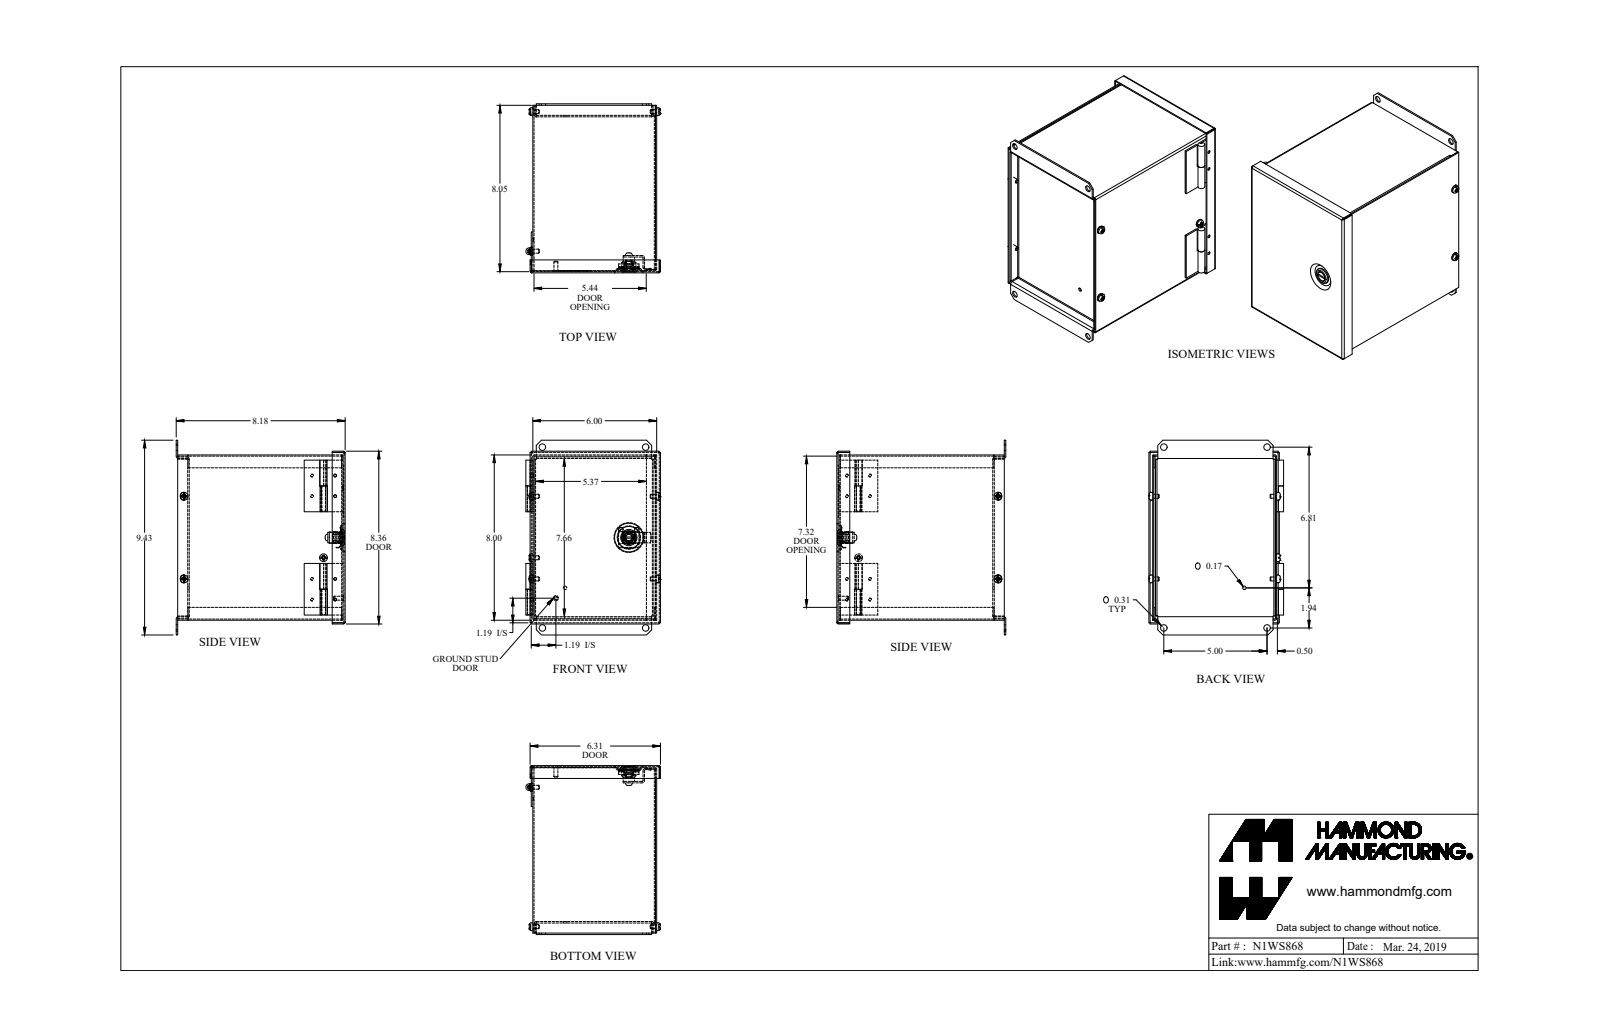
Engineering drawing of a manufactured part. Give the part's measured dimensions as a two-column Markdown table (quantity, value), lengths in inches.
| quantity | value |
| --- | --- |
| part name | N1WS868 |
| STEP written by | SolidWorks 2018 (AUTOMOTIVE_DESIGN) |
| units | inches |
| bodies | 15 solids, 539 faces (290 planar, 196 cylindrical, 53 other) |
| overall size | 9.425 × 8.179 × 6.519 |
| volume | 23.39 in³ |
| surface area | 782.9 in² |
| round holes (diameter × count) | 0.14 × 8, 0.17 × 4, 0.312 × 4, 0.187 × 1, 0.319 × 1, 0.476 × 1 |
| round bosses / shafts (diameter × count) | 0.128 × 8, 0.375 × 3, 0.19 × 3, 0.787 × 1, 0.547 × 1, 0.472 × 1, 0.469 × 1, 0.366 × 1 |
| partial cylindrical surfaces (radius × count) | 0.029 × 9, 0.086 × 9, 0.036 × 8, 0.108 × 6, 0.012 × 4, 0.1 × 4, 0.109 × 4, 0.079 × 2 |
| main face-to-face distances | 0.057, 5.943, 7.943, 6, 0.072, 5.886, 0.057, 8, 7.886, 7.564 |
| hole center spacings | 5, 1, 1.119, 1.501, 5.124, 4, 4.154, 4.45 |
